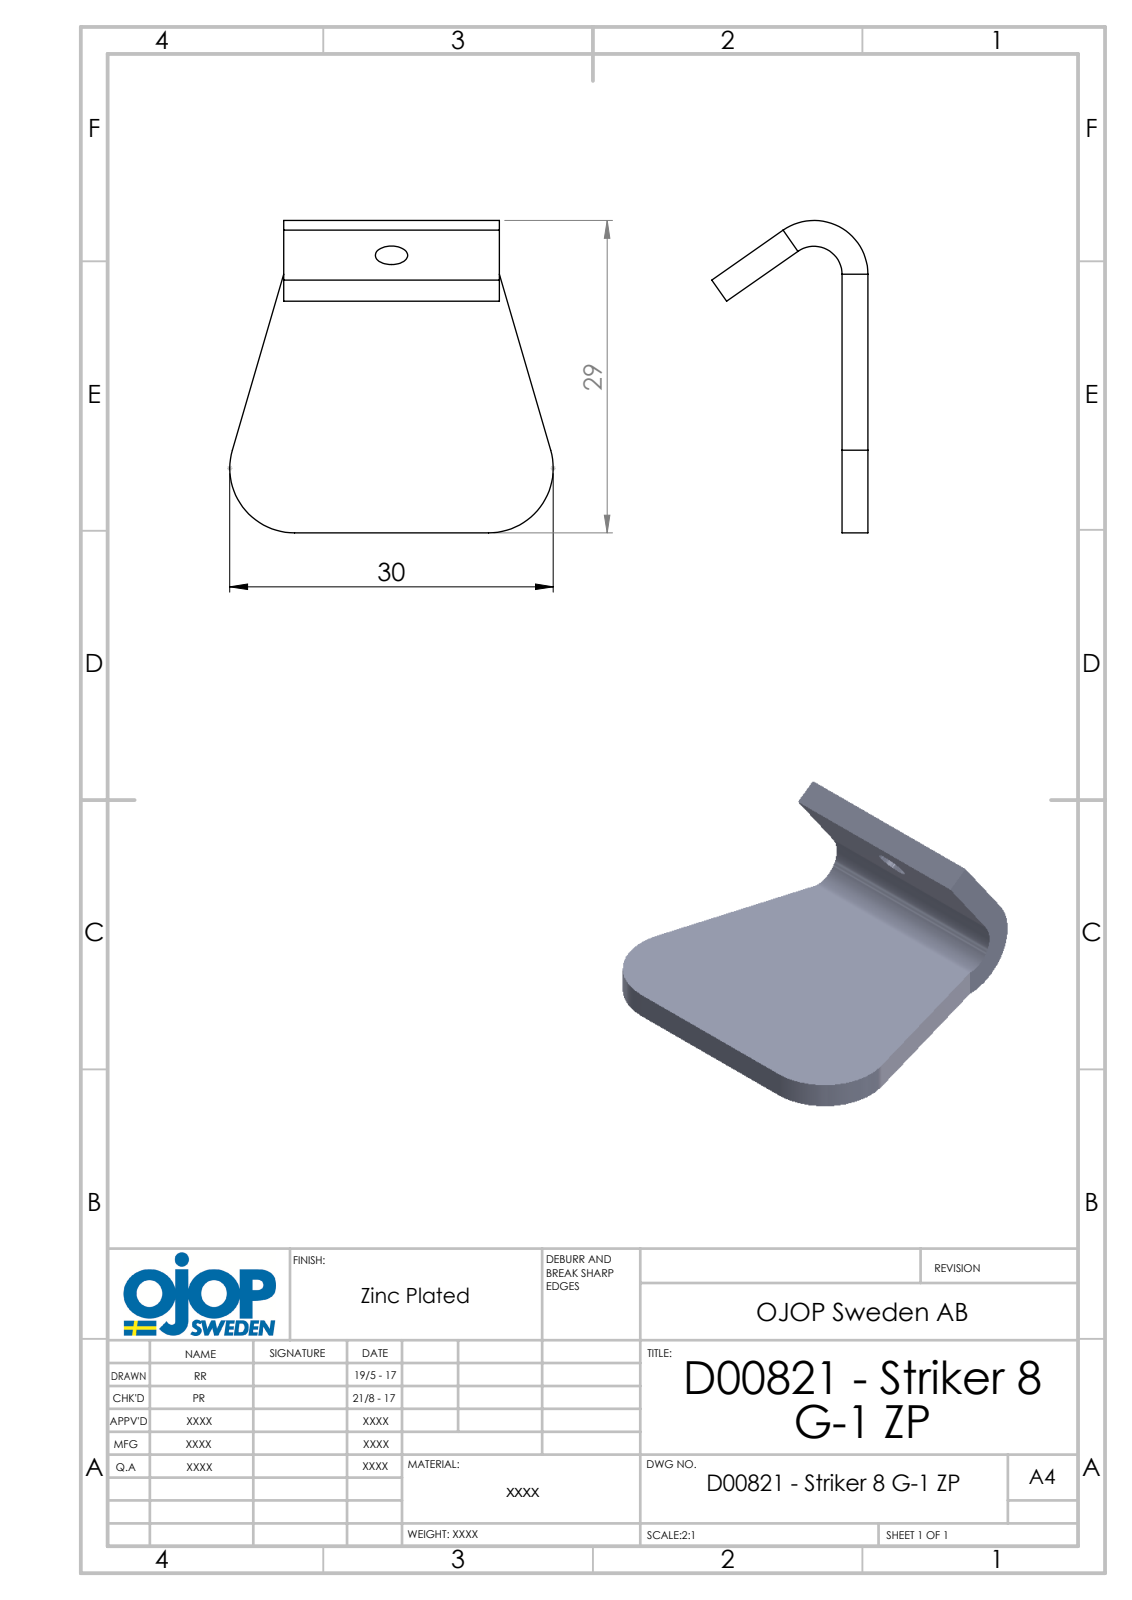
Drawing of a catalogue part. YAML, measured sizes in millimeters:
part_name: "D00821 - Striker 8 G-1 ZP"
step_written_by: "SolidWorks 2015 (AUTOMOTIVE_DESIGN)"
units: millimeters
bodies: {solids: 1, faces: 18, planar: 12, cylindrical: 6, other: 0}
overall_size: [30.5, 30, 15.55]
volume: 2498
surface_area: 2353
round_holes:
  - {diameter: 3, count: 1}
partial_cylinders:
  - {radius: 6, count: 2}
  - {radius: 3, count: 1}
  - {radius: 5.5, count: 1}
face_to_face_distances: [2.5, 20]
